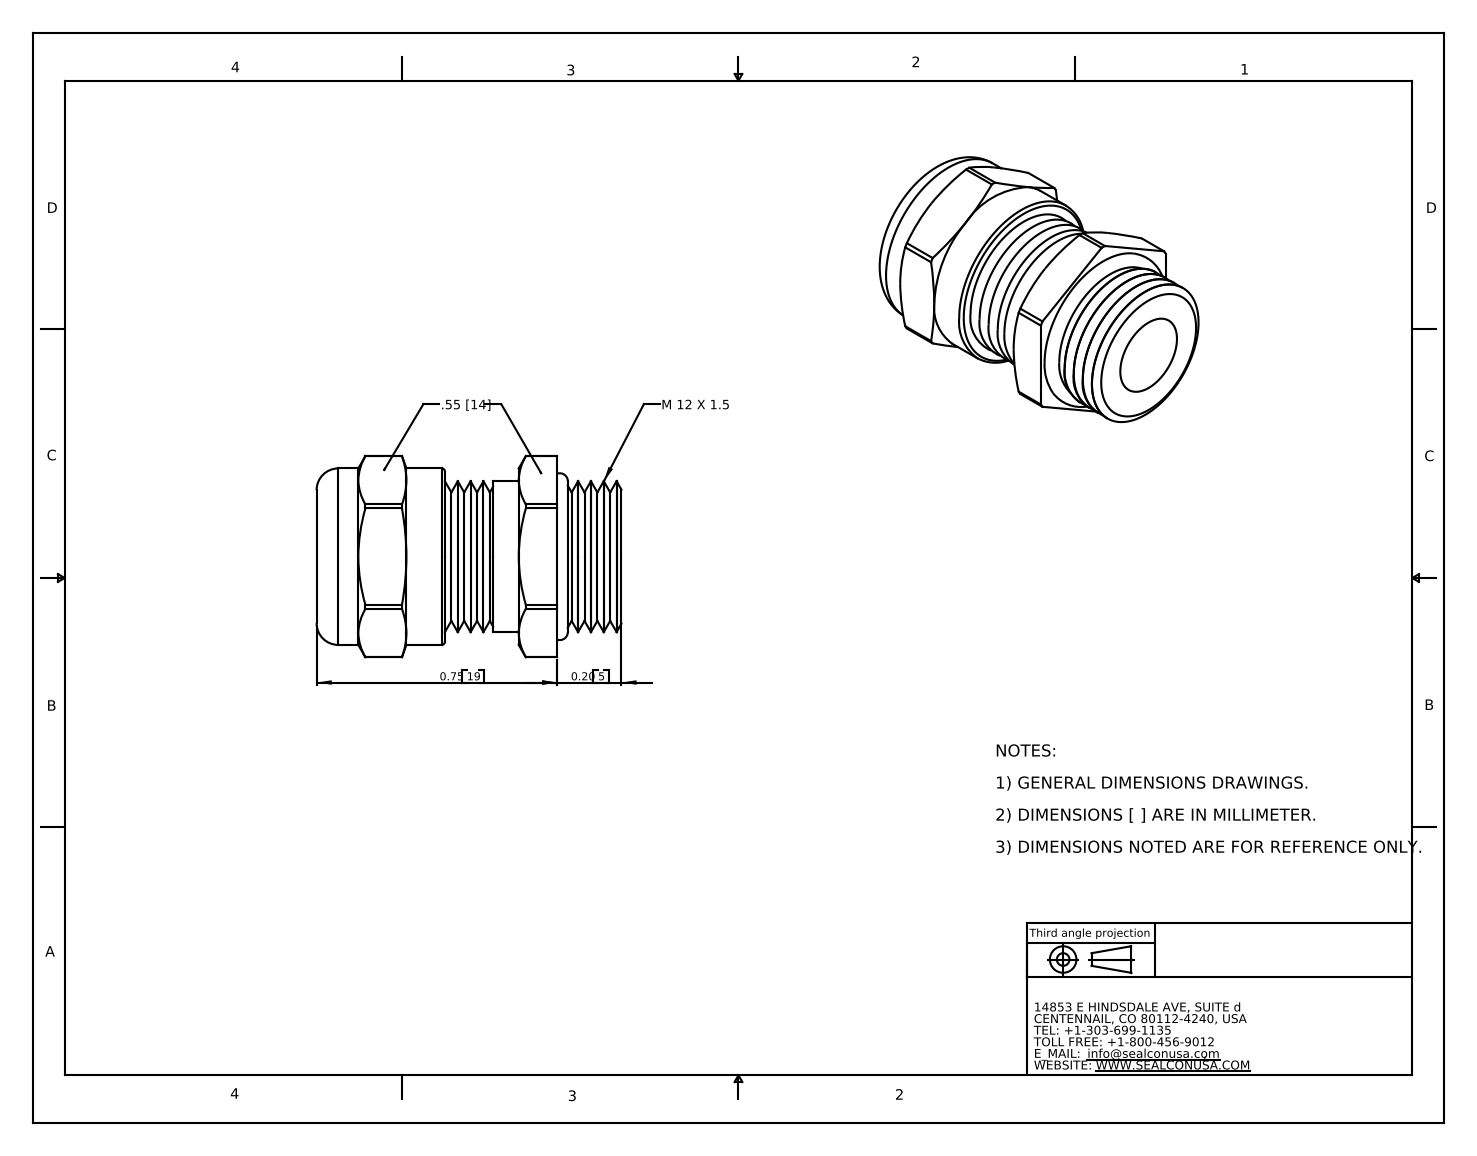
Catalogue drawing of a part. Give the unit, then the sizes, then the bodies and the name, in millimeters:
Units: millimetres
Overall size (bounding box): 24.1 × 15.9 × 14
Round holes (diameter × count): ⌀5.1 ×1, ⌀10.1 ×1, ⌀11.9 ×1
Round bosses / shafts (diameter × count): ⌀14 ×1, ⌀12 ×1
Partial cylindrical surfaces — rounded edges, fillets, slot ends (radius × count): R8 ×1
Main face-to-face distances: 14, 20.8, 12.7, 8.1, 2.8, 15.5, 23.6, 14, 18.5, 15.7
Volume: 2 620 mm³ · Surface area: 2 371 mm²
Bodies: 2 solids, 122 faces (22 planar, 28 cylindrical, 72 other)
Part name (STEP PRODUCT): CD12MR-SS
STEP written by: SolidWorks 2007 (CONFIG_CONTROL_DESIGN)
